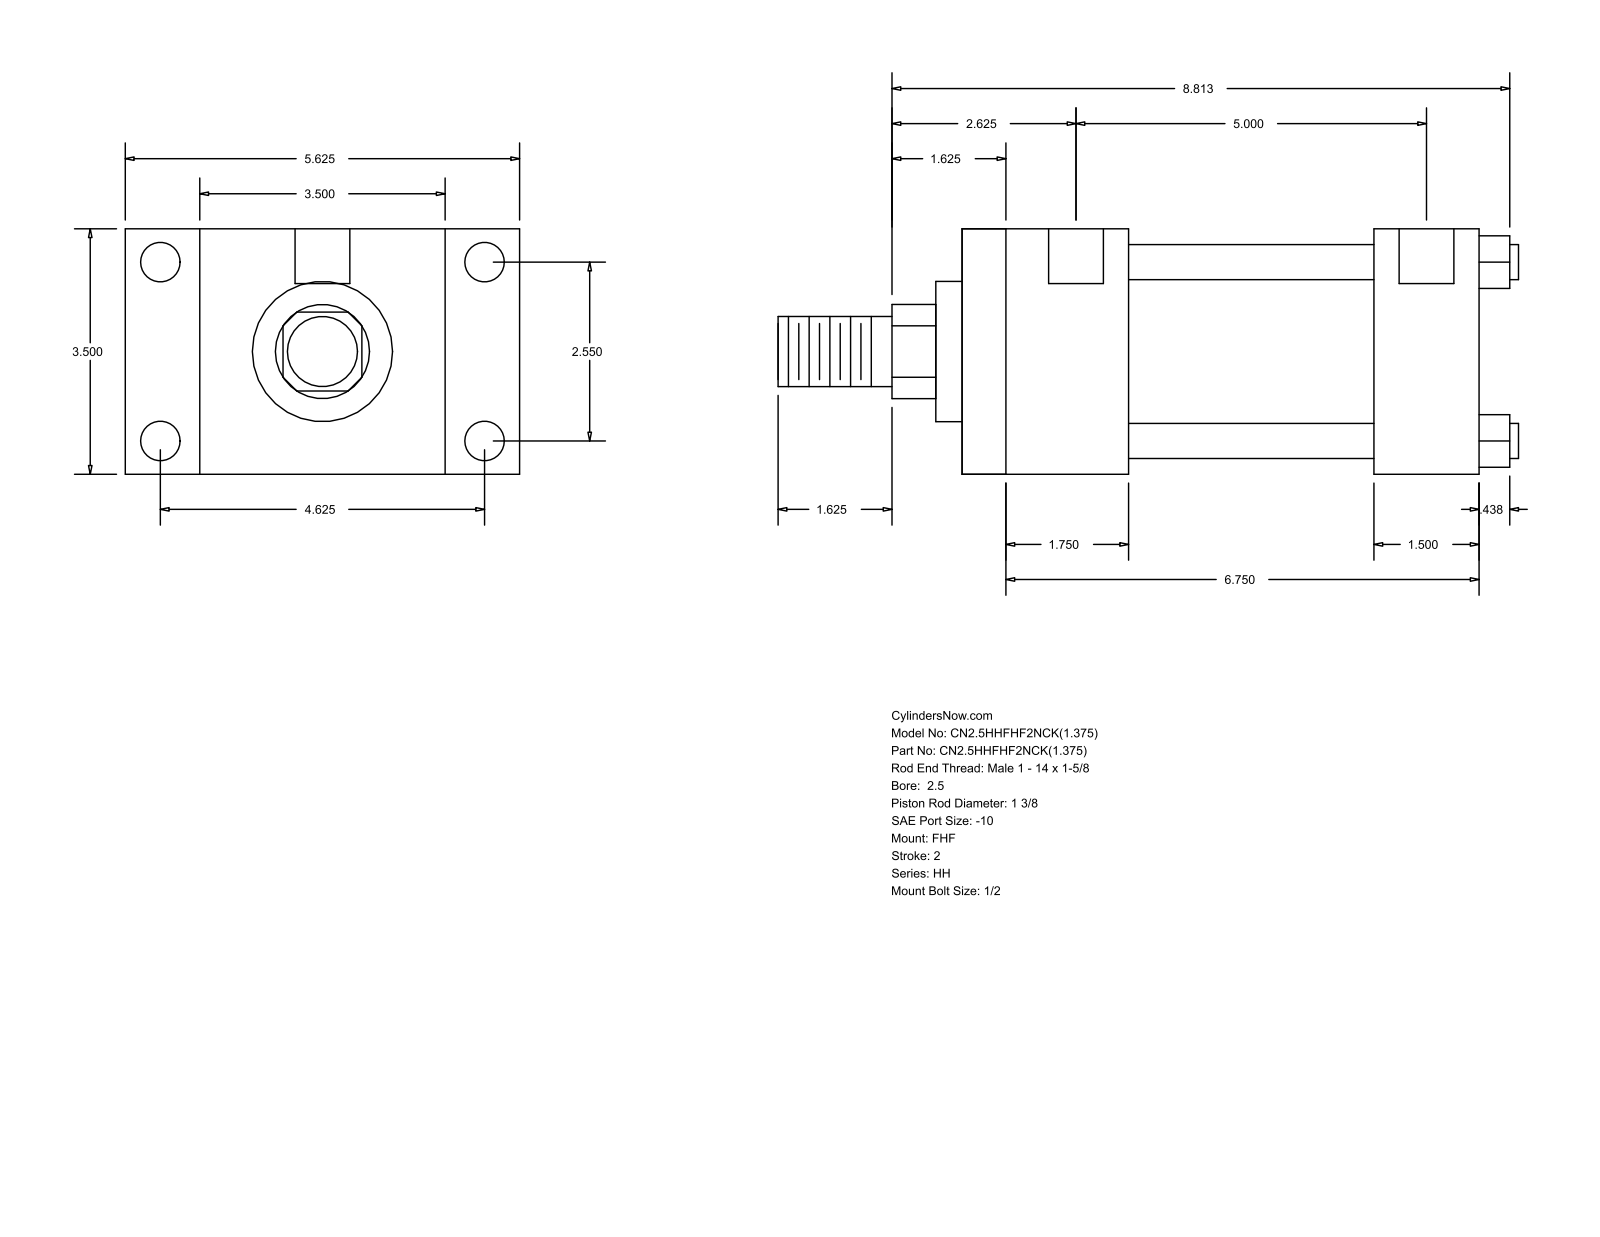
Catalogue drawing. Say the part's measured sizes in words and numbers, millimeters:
The part is named "HH_FHF__0250_1.375". Its 3-D file was written by "GSSL Pune (CONFIG_CONTROL_DESIGN)". It is 0 solids with 88 faces: 60 planar, 28 cylindrical and 0 other. Overall it measures 268.29 by 142.88 by 88.9 millimeters. Round holes: 4 of diameter 5.56, 4 of diameter 14.3, 2 of diameter 19.84. Round bosses or shafts: 4 of diameter 12.7, 1 of diameter 73.03, 1 of diameter 50.8, 1 of diameter 34.92, 1 of diameter 25.4. Partial cylindrical surfaces (rounded edges, fillets, slot ends): 1 of radius 17.06. The main face-to-face distances are 88.9, 60.32, 26.99, 115.89, 187.32, 127, 142.88, 149.22, 38.1, 19.05. The hole center spacings are 1.58, 64.76, 117.48, 128.59, 130.17, 134.15, 127.01.
